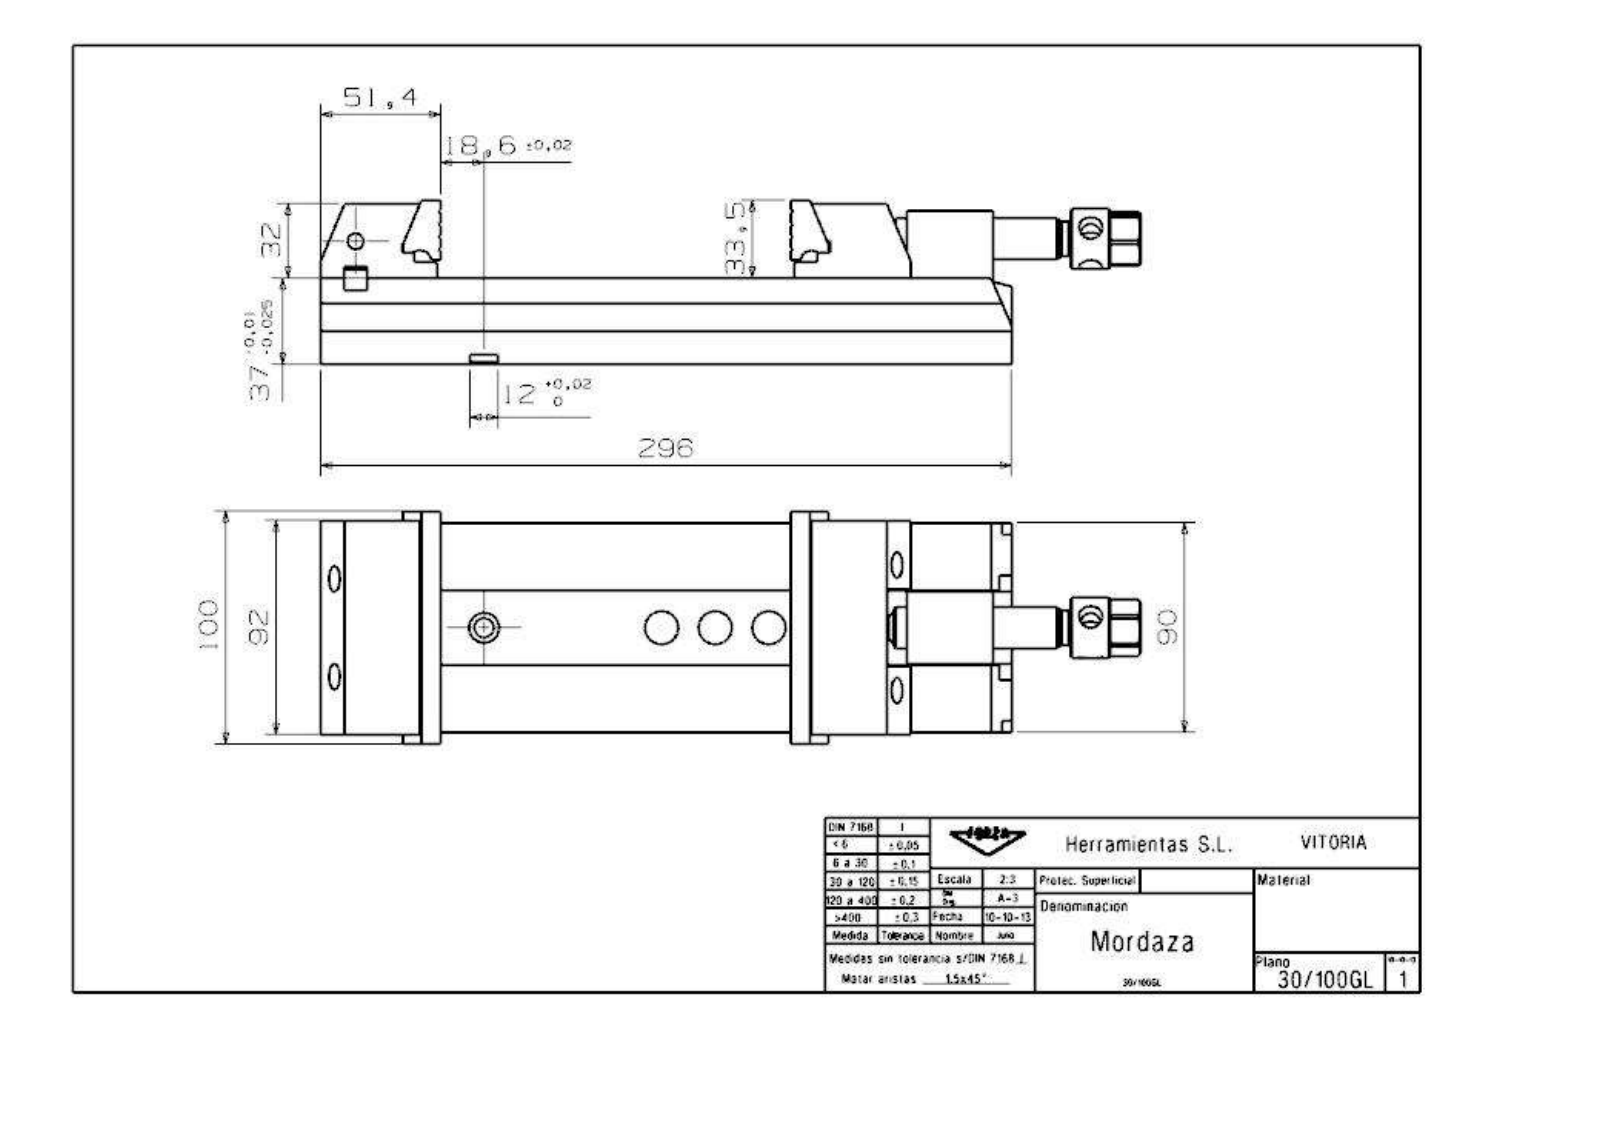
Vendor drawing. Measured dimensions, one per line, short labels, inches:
name: 30_100GL_Mordaza
written by: SIEMENS PLM Software NX 7.5 (AUTOMOTIVE_DESIGN)
unit: in
bodies: 11 solids, 405 faces (258 planar, 108 cylindrical, 39 other)
size: 13.837 × 3.937 × 2.776
volume: 61.21 in³; area: 325.7 in²
holes: 5× ⌀0.171, 5× ⌀0.275, 5× ⌀0.512, 4× ⌀0.204, 4× ⌀0.256, 4× ⌀0.295, 4× ⌀0.453, 2× ⌀0.331, 2× ⌀0.335, 2× ⌀0.394, 2× ⌀0.417, 2× ⌀0.531
bosses: 1× ⌀1.024, 1× ⌀0.698, 1× ⌀0.591, 1× ⌀0.571, 1× ⌀0.413
rounds: 16× R0.016, 5× R0.236, 4× R0.295, 2× R0.047, 2× R0.197, 2× R0.217, 1× R0.098, 1× R0.315
face distances: 1.457, 0.039, 0.543, 0.913, 0.197, 0.886, 2.461, 3.543, 2.657, 1.417
hole spacings: 1.89, 0.236, 0.237, 1.654, 2.126, 0.436, 0.437, 0.503
